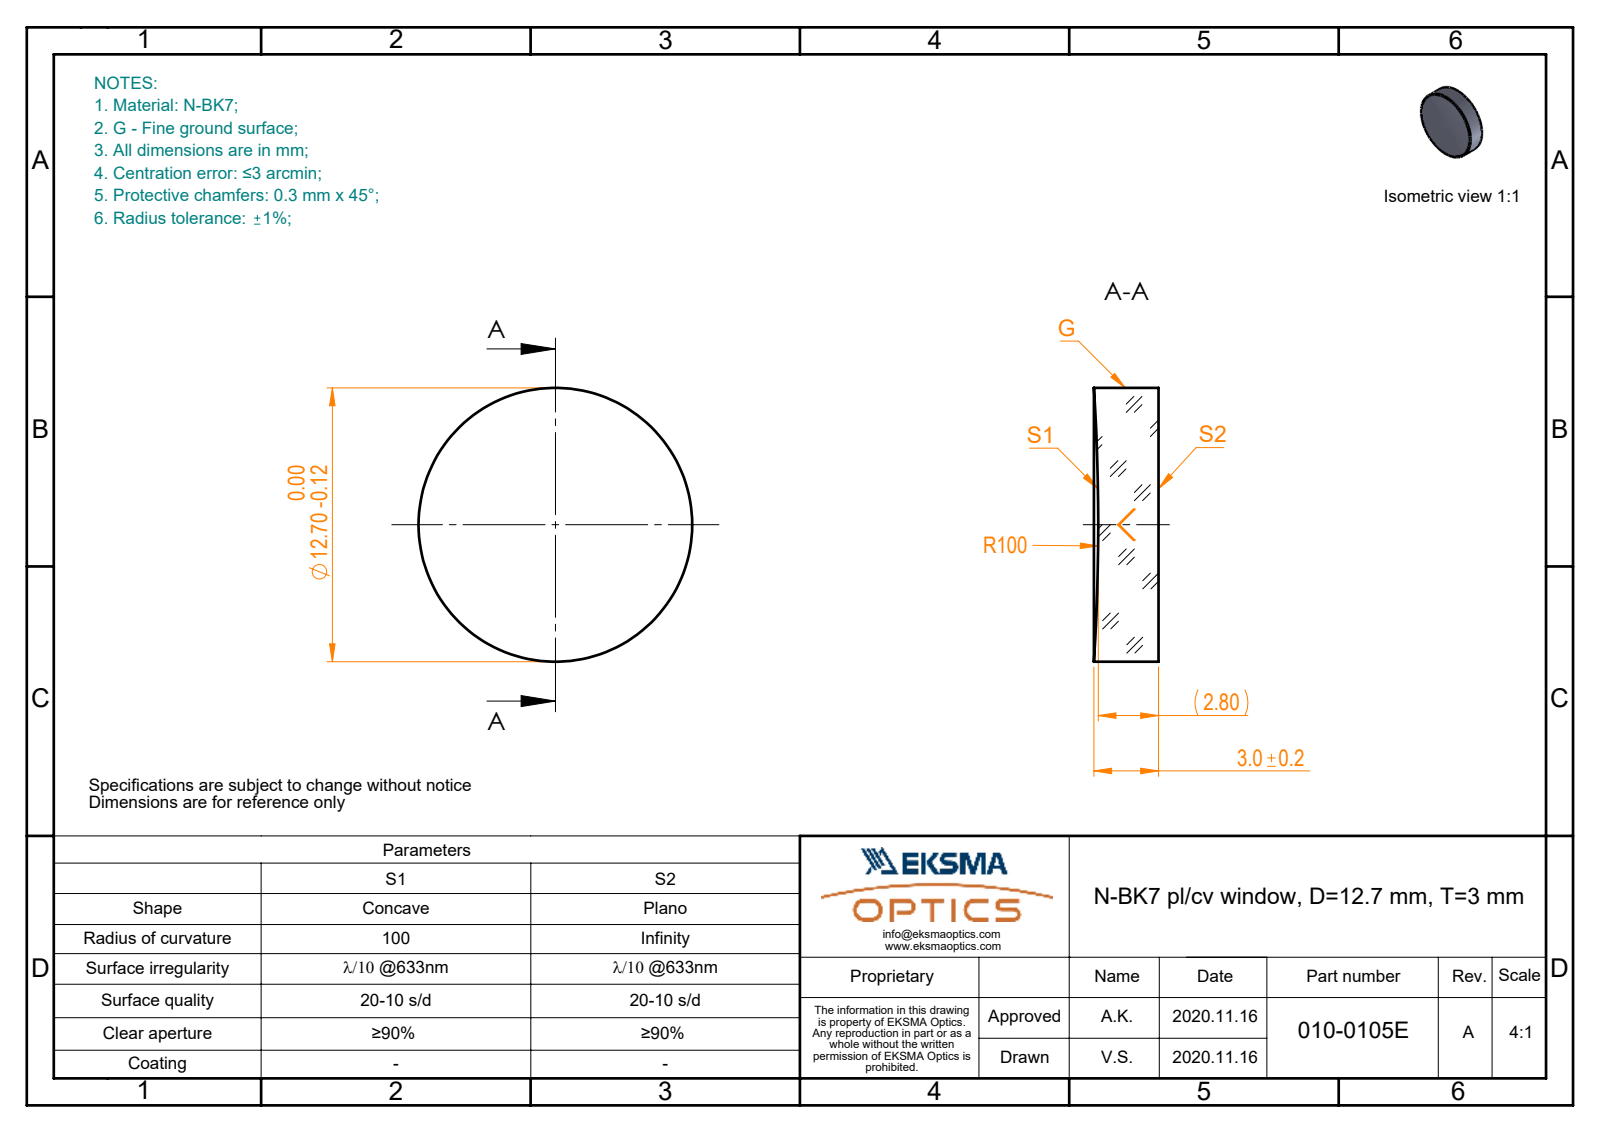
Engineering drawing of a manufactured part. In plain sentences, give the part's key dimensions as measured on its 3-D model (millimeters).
The part is named "010-0105E_N-BK7_PCV_window". Its 3-D file was written by "SolidWorks 2019 (CONFIG_CONTROL_DESIGN)". It is 1 solid with 5 faces: 1 planar, 2 cylindrical and 2 other. Overall it measures 12.7 by 12.7 by 3 millimeters. Its volume is 367 cubic millimeters and its surface area 373 square millimeters. Round bosses or shafts: 1 of diameter 12.7.
